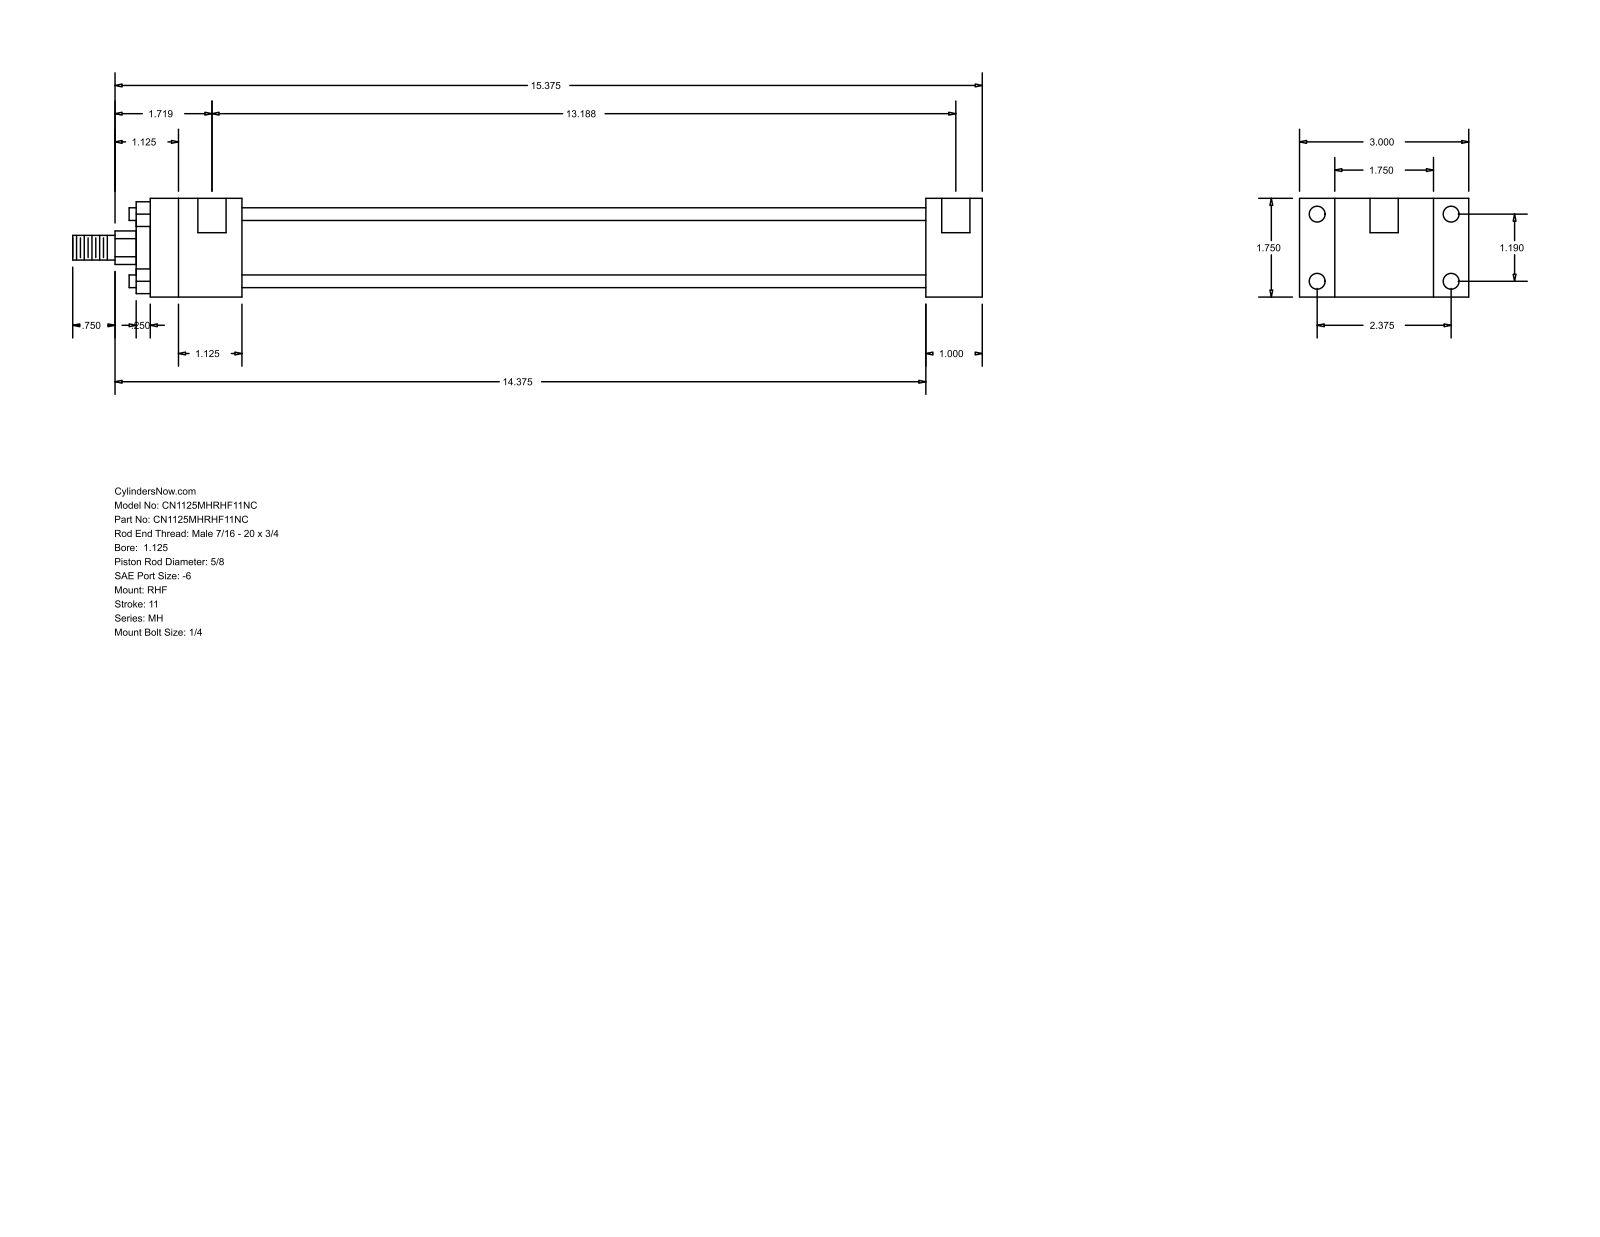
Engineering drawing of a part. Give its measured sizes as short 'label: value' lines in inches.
name: MH_RHF__0112_0.625
written by: GSSL Pune (CONFIG_CONTROL_DESIGN)
unit: in
bodies: 0 solids, 88 faces (60 planar, 28 cylindrical, 0 other)
size: 16.125 × 3 × 1.75
holes: 4× ⌀0.219, 4× ⌀0.281, 2× ⌀0.5
bosses: 4× ⌀0.225, 1× ⌀1.375, 1× ⌀1.125, 1× ⌀0.625, 1× ⌀0.437
rounds: 1× R0.297
face distances: 1.75, 0.625, 1, 2.375, 3, 12.125, 13.125, 1.625, 13.75, 14.75
hole spacings: 1.19, 2.375, 2.656, 13.063, 0.125, 13.187
